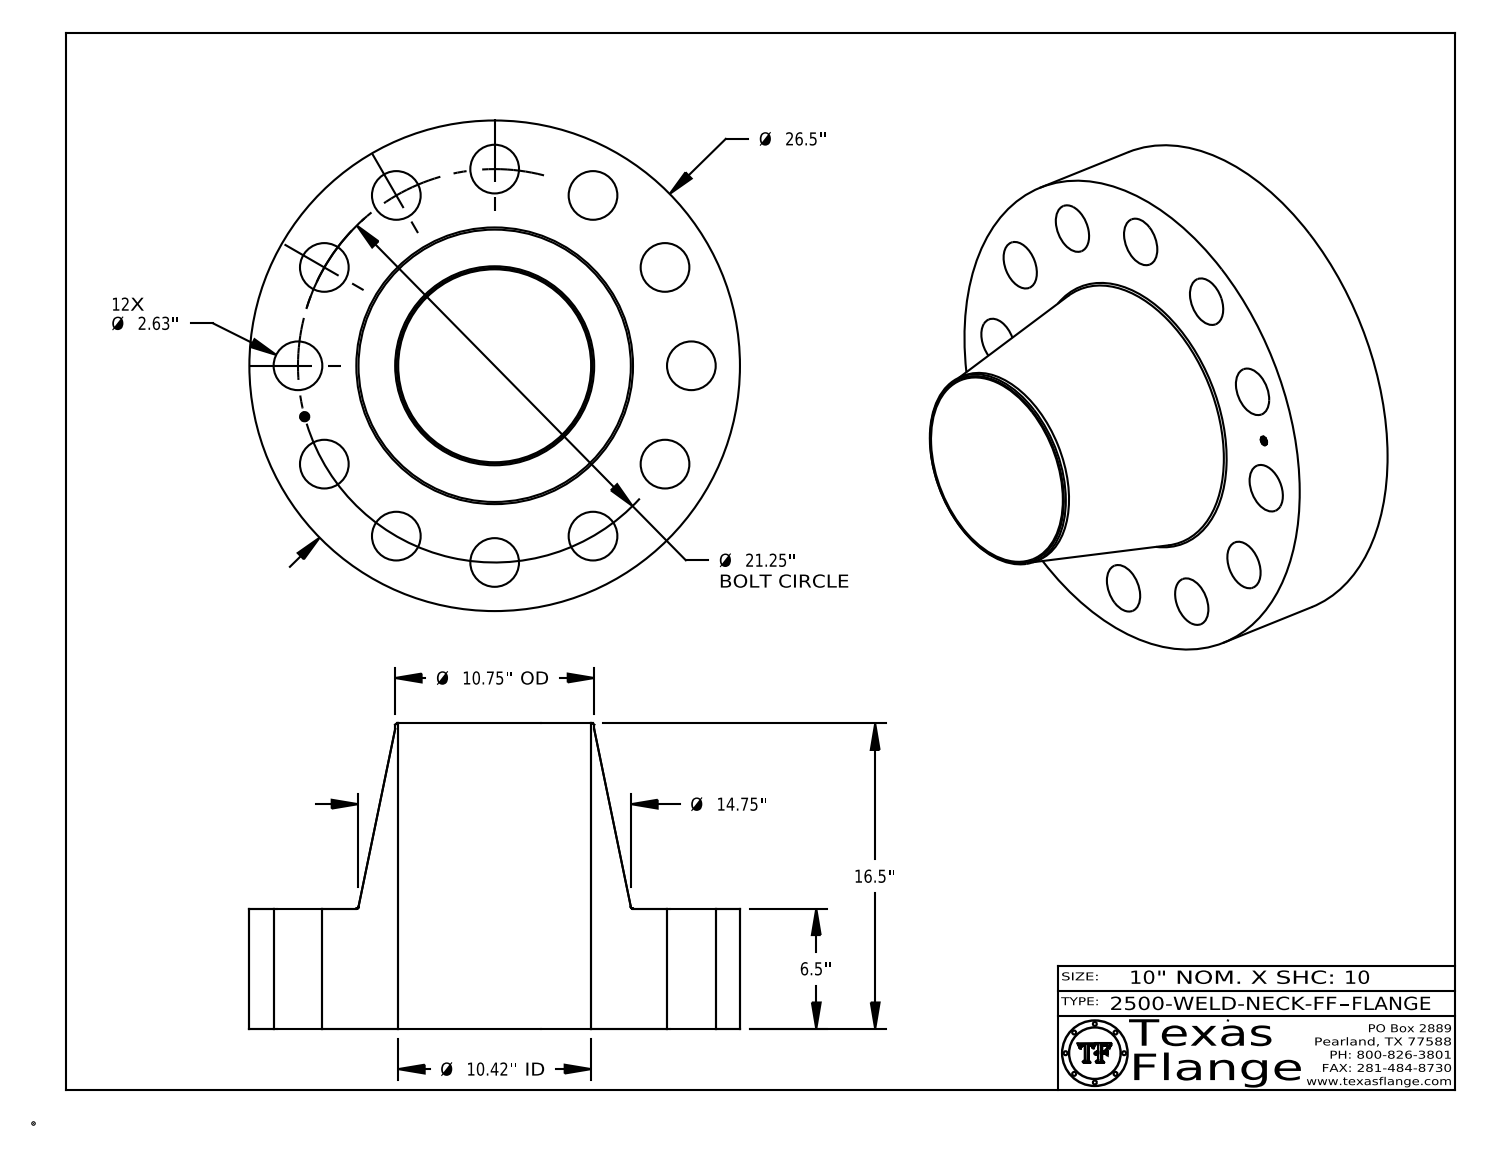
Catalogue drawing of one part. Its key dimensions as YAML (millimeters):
part_name: "2500-WELD-NECK-FF"
step_written_by: "CATIA V5 STEP AP214 (AUTOMOTIVE_DESIGN)"
units: millimeters
bodies: {solids: 1, faces: 424, planar: 368, cylindrical: 50, other: 6}
overall_size: [673.1, 673.1, 419.1]
volume: 49650000
surface_area: 1840000
round_holes:
  - {diameter: 66.8, count: 12}
  - {diameter: 12.6, count: 1}
  - {diameter: 264.7, count: 1}
round_bosses_or_shafts:
  - {diameter: 0.8, count: 8}
  - {diameter: 673.1, count: 1}
  - {diameter: 273.1, count: 1}
  - {diameter: 9.9, count: 1}
face_to_face_distances: [165.1, 419.1, 254, 164.7, 0.4, 254.4, 3.8, 3.7, 0.7, 2.4]
hole_center_spacings: [269.9, 139.7, 467.4, 381.7, 521.4, 381.7, 521.4, 539.8]
